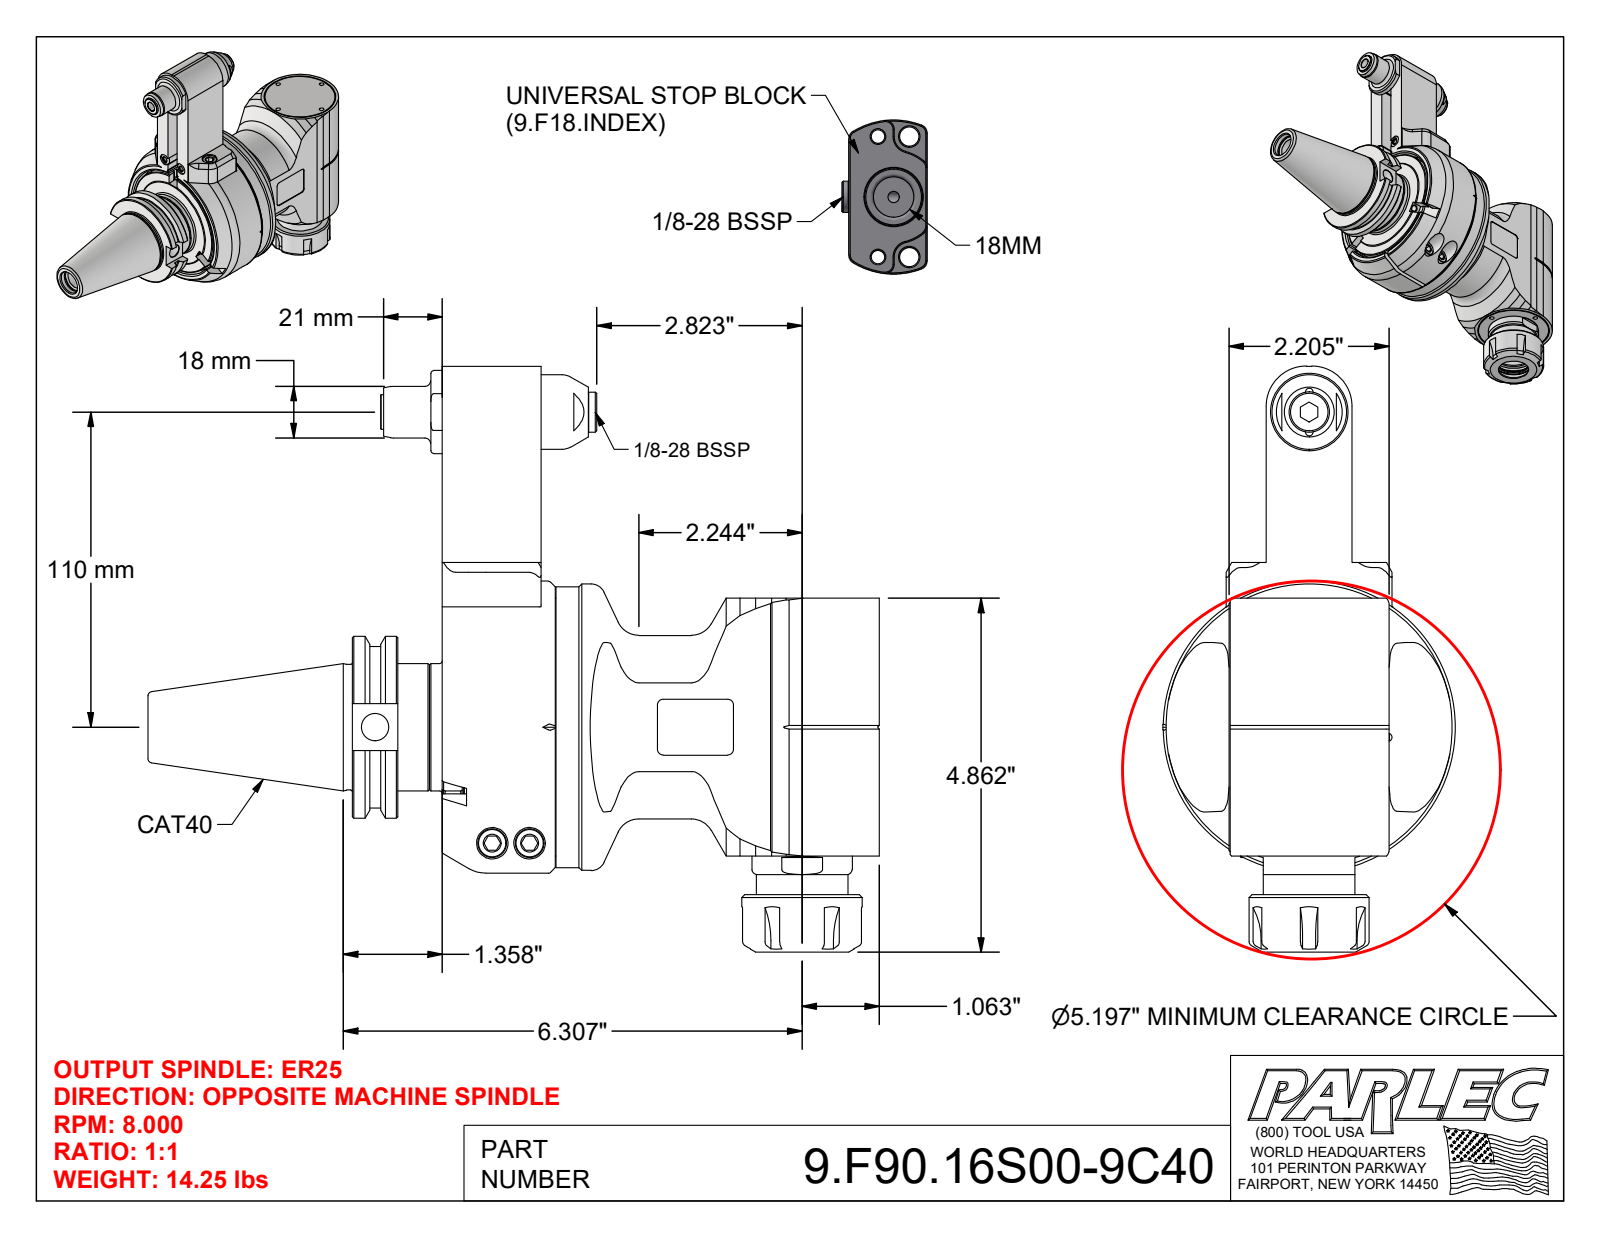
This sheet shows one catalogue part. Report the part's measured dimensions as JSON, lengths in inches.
{"part_name": "9.F90.16S00-9C40; 9GA11C_441 (Type 1, Cat40, 110mm); 9_F90_16S00", "step_written_by": "Autodesk Inventor 2022 (AUTOMOTIVE_DESIGN)", "units": "inches", "bodies": {"solids": 4, "faces": 647, "planar": 281, "cylindrical": 171, "other": 195}, "overall_size": [10.057, 8.051, 4.016], "volume_in3": 62.86, "surface_area_in2": 236.6, "round_holes": [[0.126, 8], [0.165, 4], [0.256, 3], [0.102, 2], [0.13, 2], [0.197, 2], [0.315, 2], [0.409, 2], [0.433, 2], [0.492, 2], [1.063, 2], [0.098, 1]], "round_bosses_or_shafts": [[0.394, 4], [0.709, 2], [0.472, 2], [0.315, 2], [0.236, 2], [0.098, 2], [4.016, 1], [3.937, 1]], "partial_cylinders_radius": [[0.039, 14], [0.079, 12], [0.118, 6], [0.984, 6], [0.157, 4], [0.016, 2], [0.02, 2], [0.315, 2]], "face_to_face_distances": [1.26, 0.512, 1.28, 1.693, 0.02, 0.276, 1.555, 0.335, 1.252, 0.303], "hole_center_spacings": [0.325, 0.459, 0.846, 1.197, 0.276, 0.65, 1.646, 1.674]}
